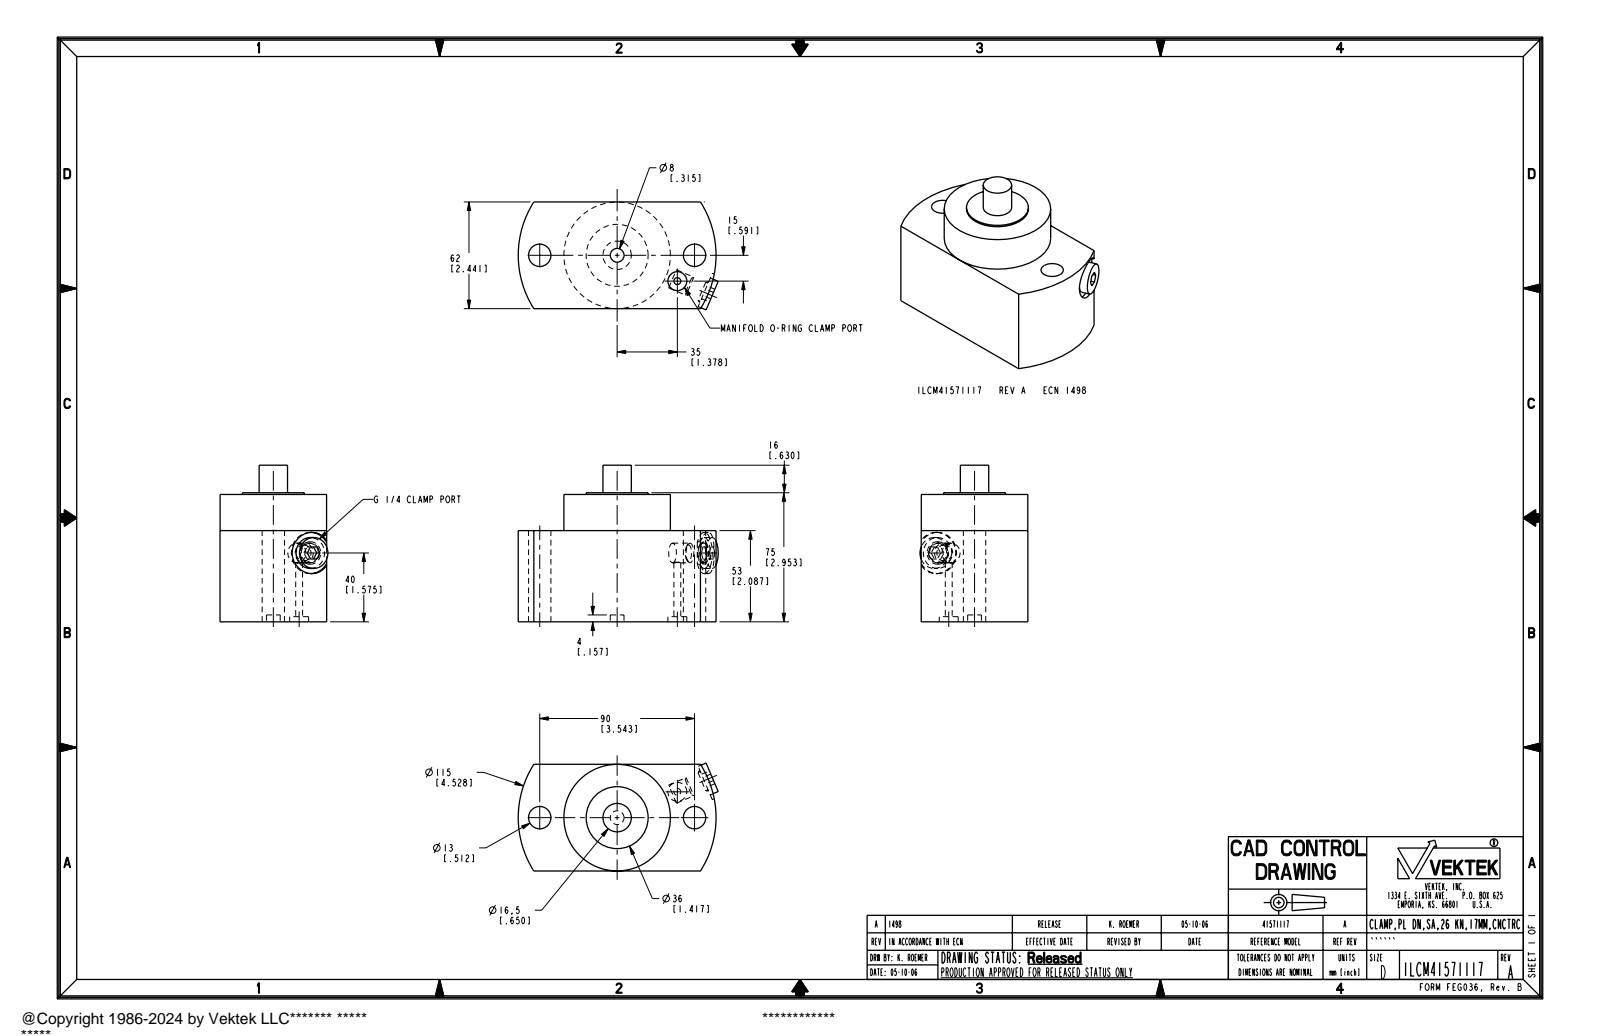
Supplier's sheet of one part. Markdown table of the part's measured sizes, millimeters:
| quantity | value |
| --- | --- |
| part name | ILCM41571117 |
| STEP written by | PRO/ENGINEER BY PARAMETRIC TECHNOLOGY CORPORATION, 2004290 (AUTOMOTIVE_DESIGN_CC2) |
| units | millimeters |
| bodies | 1 solid, 52 faces (21 planar, 27 cylindrical, 4 other) |
| overall size | 116.25 × 91 × 62.73 |
| volume | 410 403 mm³ |
| surface area | 41 418 mm² |
| round holes (diameter × count) | 13 × 2, 4 × 1, 8 × 1, 11 × 1, 11.45 × 1, 24 × 1 |
| round bosses / shafts (diameter × count) | 61.9 × 1, 36 × 1, 18 × 1, 16.5 × 1, 11.45 × 1 |
| partial cylindrical surfaces (radius × count) | 57.5 × 1 |
| main face-to-face distances | 62, 53, 74, 21, 1, 75, 22, 91, 38, 17 |
| hole center spacings | 45, 18.03, 38.08, 81.39, 90 |
